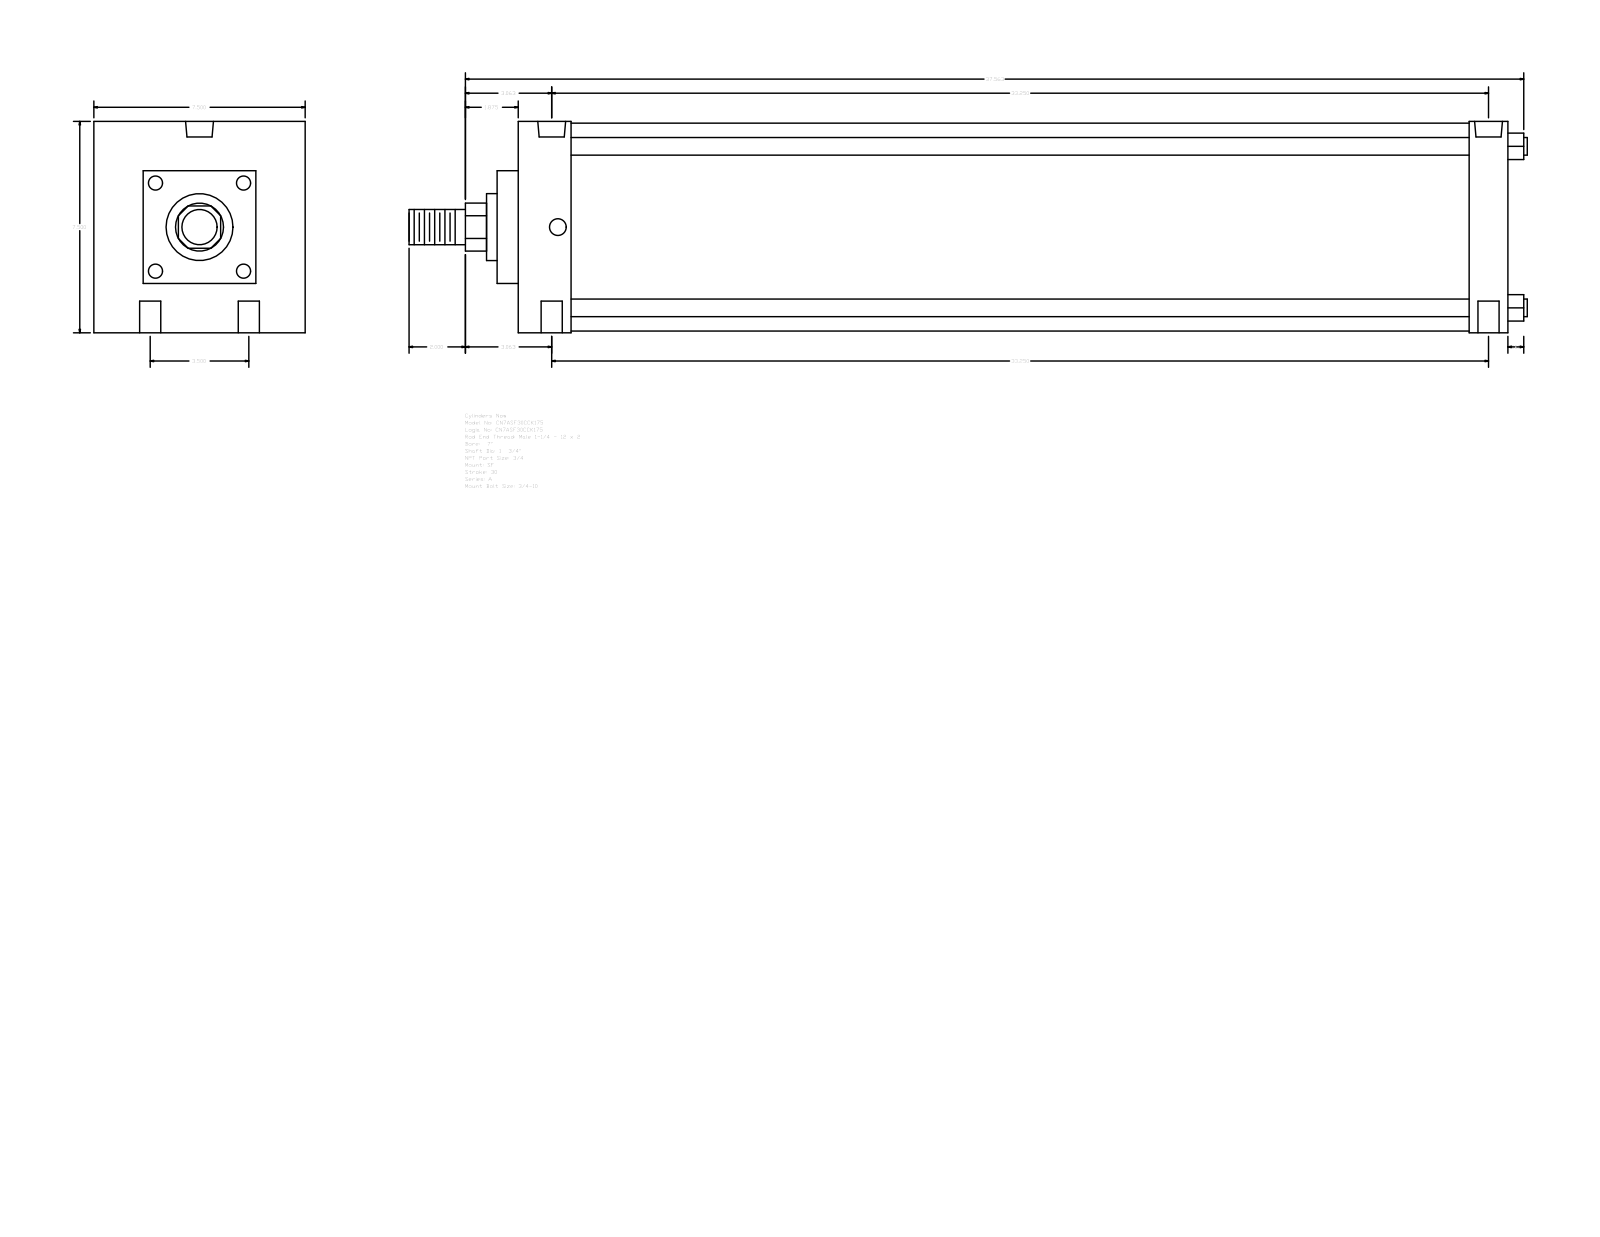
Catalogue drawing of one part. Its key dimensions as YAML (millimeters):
part_name: "A_SF__0700_1.75"
step_written_by: "GSSL Pune (CONFIG_CONTROL_DESIGN)"
units: millimeters
bodies: {solids: 0, faces: 93, planar: 67, cylindrical: 26, other: 0}
overall_size: [1008.06, 190.5, 190.5]
round_holes:
  - {diameter: 19.05, count: 4}
  - {diameter: 15.08, count: 2}
  - {diameter: 25.12, count: 2}
round_bosses_or_shafts:
  - {diameter: 15.88, count: 4}
  - {diameter: 187.32, count: 1}
  - {diameter: 60.33, count: 1}
  - {diameter: 44.45, count: 1}
  - {diameter: 31.75, count: 1}
partial_cylinders:
  - {radius: 21.63, count: 1}
face_to_face_distances: [190.5, 892.18, 146.05, 19.05, 47.63, 857.26, 809.63, 844.55, 34.92, 44.45]
hole_center_spacings: [44.45, 845.72, 844.55, 88.9, 849.22, 833.43]
